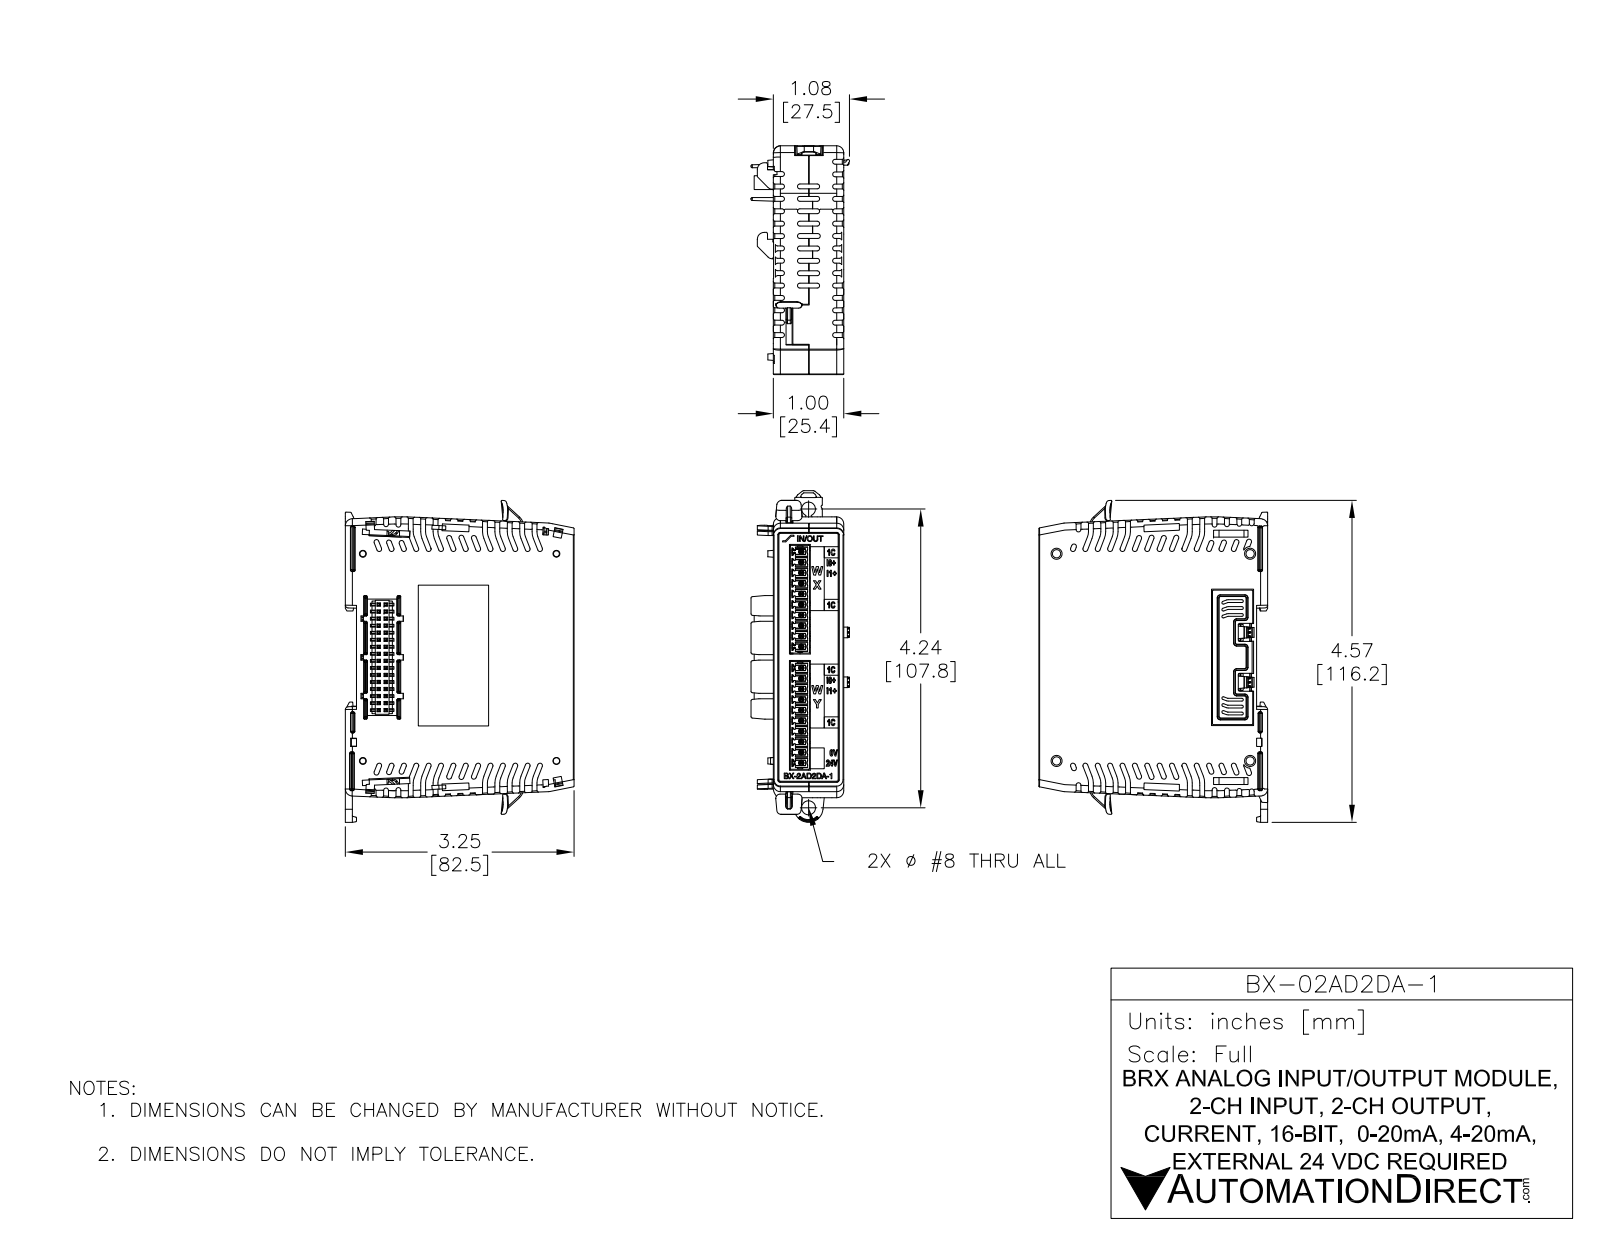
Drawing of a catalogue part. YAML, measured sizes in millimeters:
part_name: "BX-2AD2DA-1"
step_written_by: "SolidWorks 2017 (AUTOMOTIVE_DESIGN)"
units: millimeters
bodies: {solids: 10, faces: 4499, planar: 3215, cylindrical: 627, other: 657}
overall_size: [116.5, 82.6, 35.6]
volume: 155000
surface_area: 57420
round_holes:
  - {diameter: 0.4, count: 8}
  - {diameter: 0.4, count: 2}
  - {diameter: 3, count: 2}
  - {diameter: 3, count: 2}
  - {diameter: 5.1, count: 1}
round_bosses_or_shafts:
  - {diameter: 2.8, count: 2}
  - {diameter: 1.5, count: 2}
  - {diameter: 1.8, count: 1}
partial_cylinders:
  - {radius: 0.5, count: 109}
  - {radius: 0.2, count: 103}
  - {radius: 0.1, count: 48}
  - {radius: 1.6, count: 20}
  - {radius: 0.3, count: 16}
  - {radius: 0.4, count: 16}
  - {radius: 0.3, count: 14}
  - {radius: 0.2, count: 12}
face_to_face_distances: [25.4, 21.2, 4.2, 77.5, 5.3, 15.9, 20.1, 77.8, 52.1, 25.7]
hole_center_spacings: [3.8, 7.6, 11.4, 15.2, 19.1, 41.9, 22.9, 38.1]
